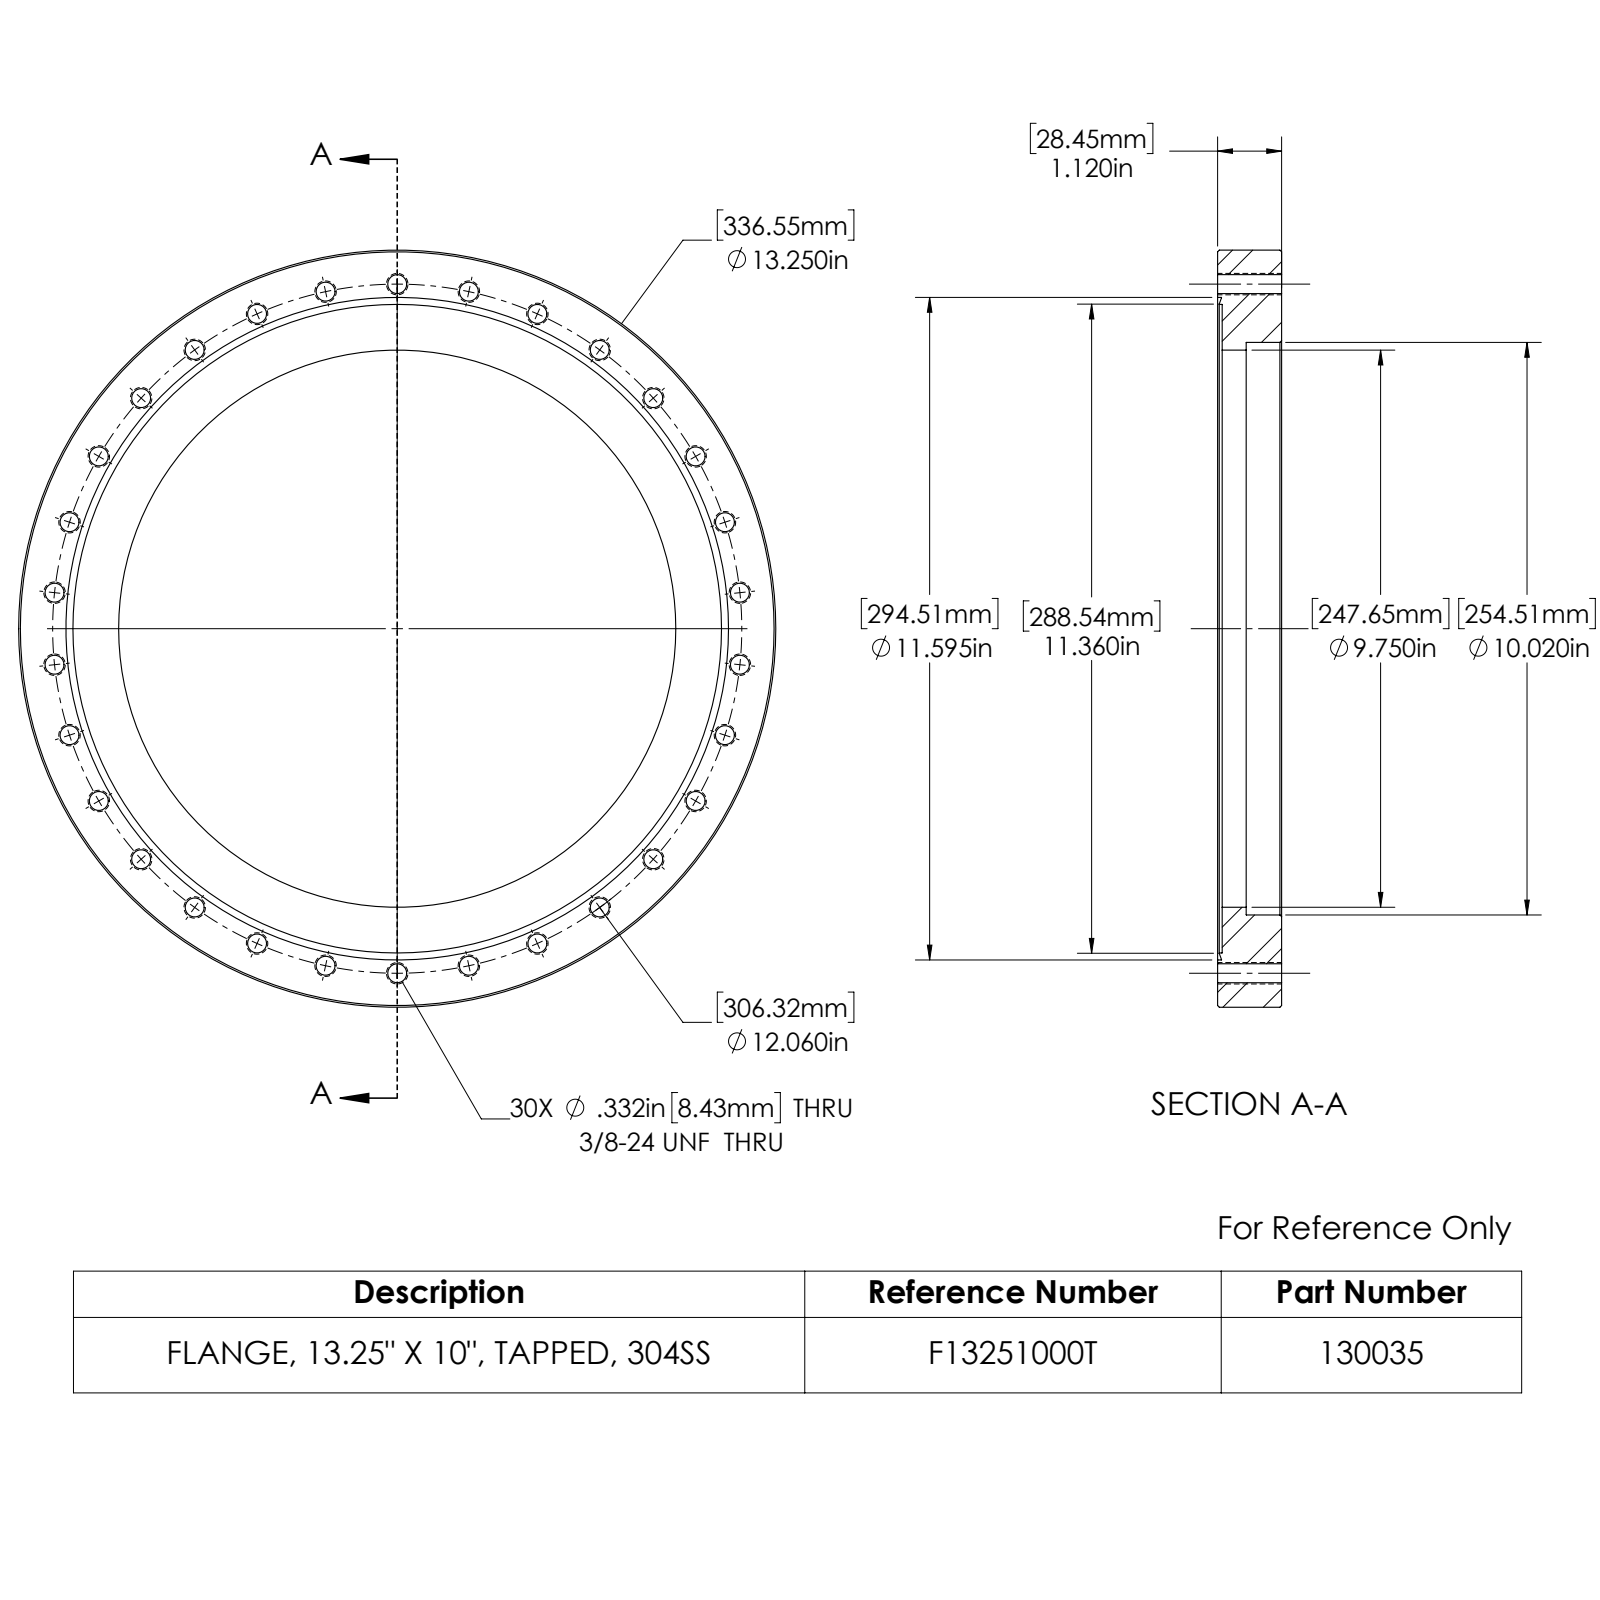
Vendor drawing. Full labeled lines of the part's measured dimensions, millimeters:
Part name (STEP PRODUCT): 130035_C
STEP written by: SolidWorks 2022 (CONFIG_CONTROL_DESIGN)
Units: millimetres
Bodies: 1 solid, 90 faces (4 planar, 70 cylindrical, 16 other)
Overall size (bounding box): 336.6 × 336.6 × 28.4
Volume: 1 031 000 mm³ · Surface area: 153 300 mm²
Round holes (diameter × count): ⌀8.4 ×30, ⌀247.7 ×1, ⌀254.5 ×1, ⌀288.3 ×1, ⌀294.5 ×1
Round bosses / shafts (diameter × count): ⌀336.6 ×1
Main face-to-face distances: 28.4, 2, 26.4, 12.7, 10.7, 15.7
Hole centre spacings: 94.7, 304.6, 205, 299.6, 247.8, 279.8, 124.6, 180.1
